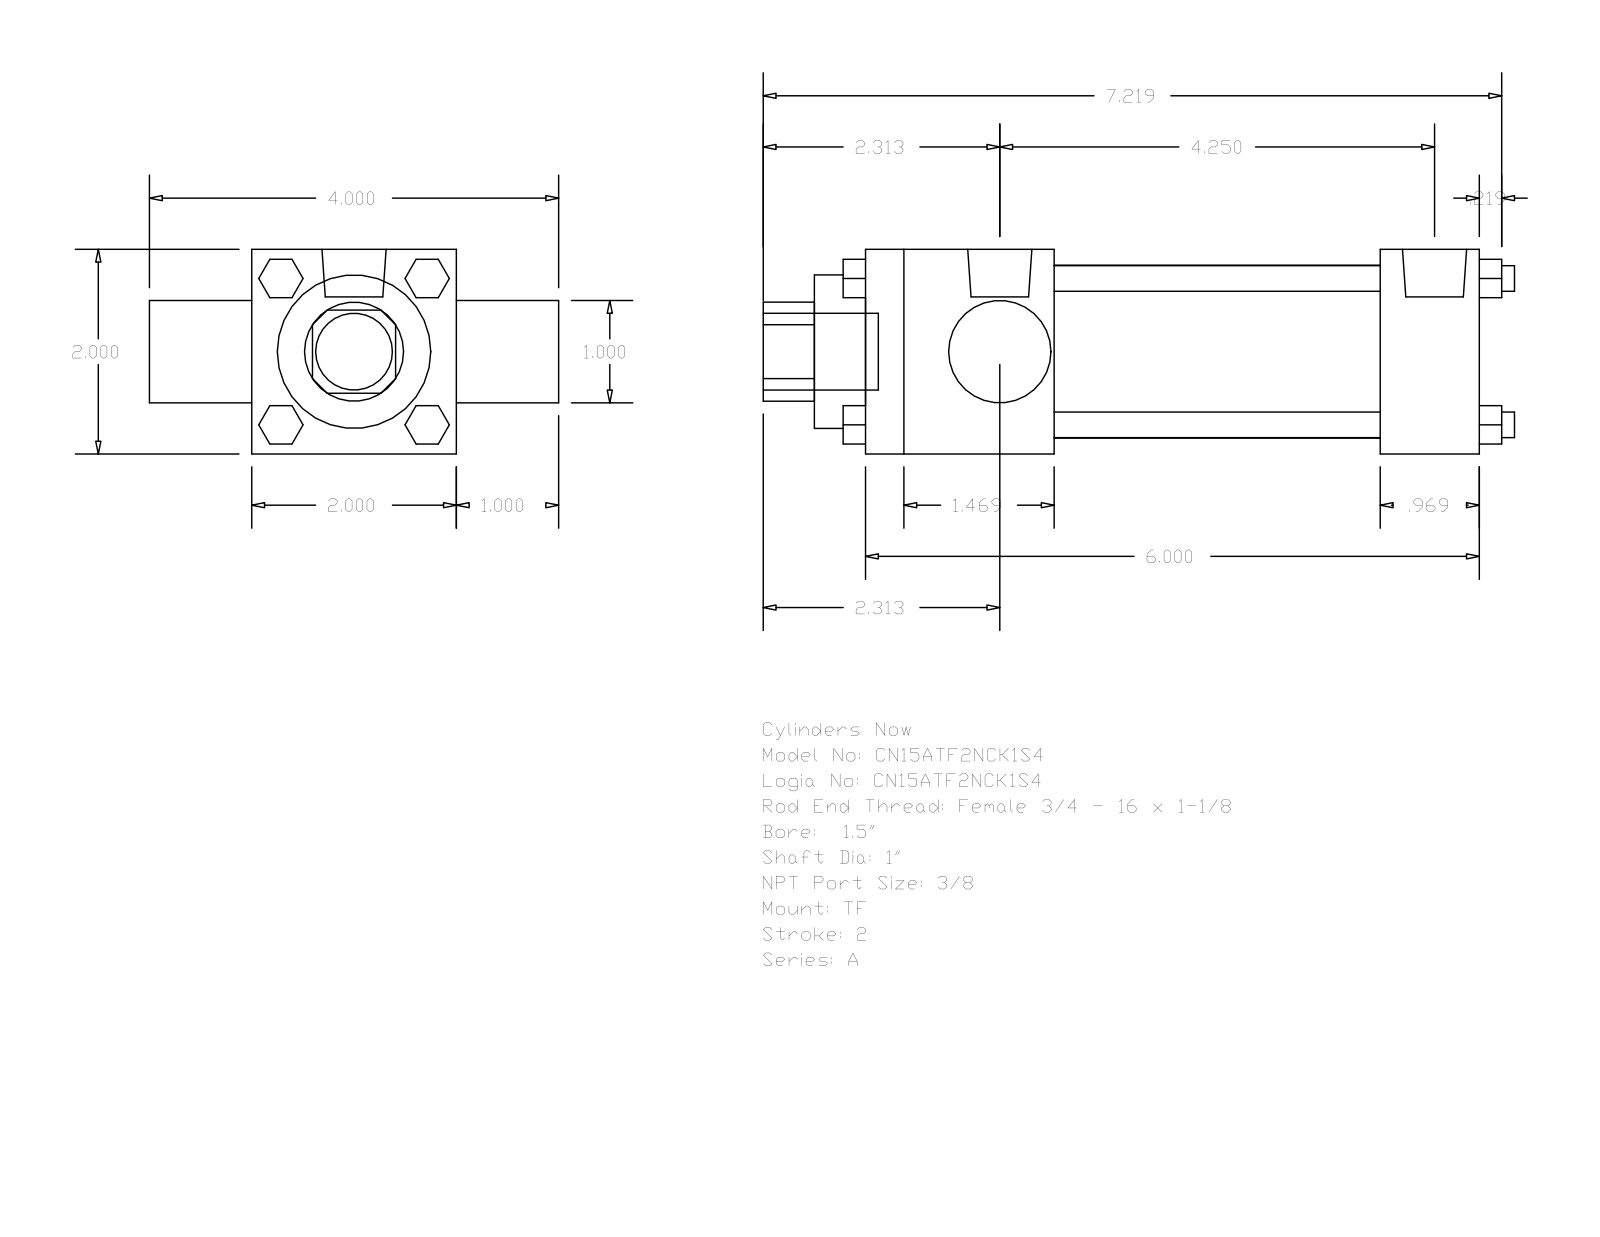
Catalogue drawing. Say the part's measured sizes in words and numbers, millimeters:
The part is named "A_TF__0150_1". Its 3-D file was written by "GSSL Pune (CONFIG_CONTROL_DESIGN)". It is 0 solids with 120 faces: 92 planar, 28 cylindrical and 0 other. Overall it measures 186.53 by 101.6 by 50.8 millimeters. Round holes: 2 of diameter 25.4, 1 of diameter 38.1, 1 of diameter 42.93. Round bosses or shafts: 4 of diameter 6.35, 3 of diameter 5.56, 2 of diameter 15.93, 1 of diameter 19.05. Partial cylindrical surfaces (rounded edges, fillets, slot ends): 1 of radius 12.29. The main face-to-face distances are 50.8, 25.4, 152.4, 76.2, 46.83, 127.79, 80.96, 105.57, 24.61, 12.7.
